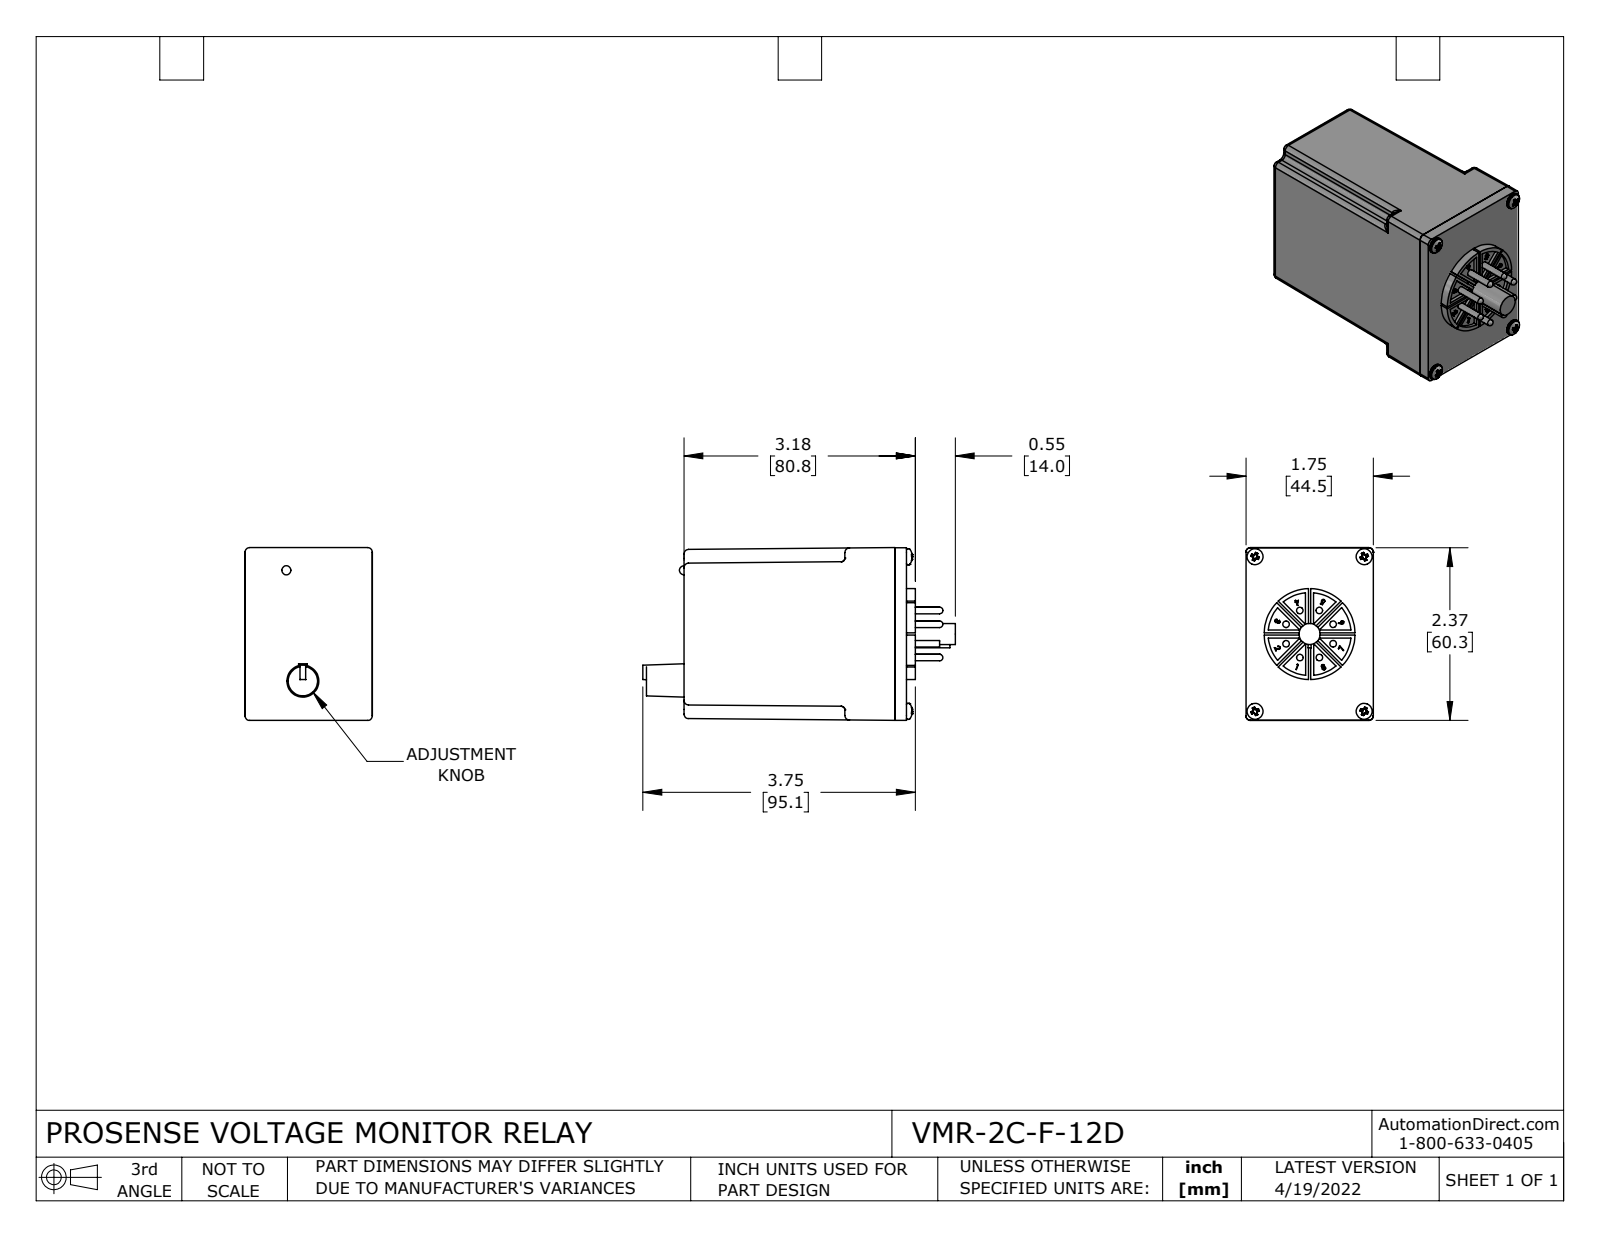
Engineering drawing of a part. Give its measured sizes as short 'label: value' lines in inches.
name: VMR-2C-F-12D
written by: SolidWorks 2021 (CONFIG_CONTROL_DESIGN)
unit: in
bodies: 17 solids, 542 faces (221 planar, 164 cylindrical, 157 other)
size: 4.295 × 2.375 × 1.75
volume: 12.33 in³; area: 45.79 in²
holes: 4× ⌀0.125
bosses: 8× ⌀0.09, 4× ⌀0.219, 1× ⌀1.25, 1× ⌀0.29
rounds: 32× R0.063, 8× R0.005, 4× R0.05, 1× R0.57
face distances: 2.9, 0.16, 3.06, 0.07, 0.23, 3.13, 0.188, 0.05, 0.12, 0.28
hole spacings: 1.5, 2.125, 2.601
